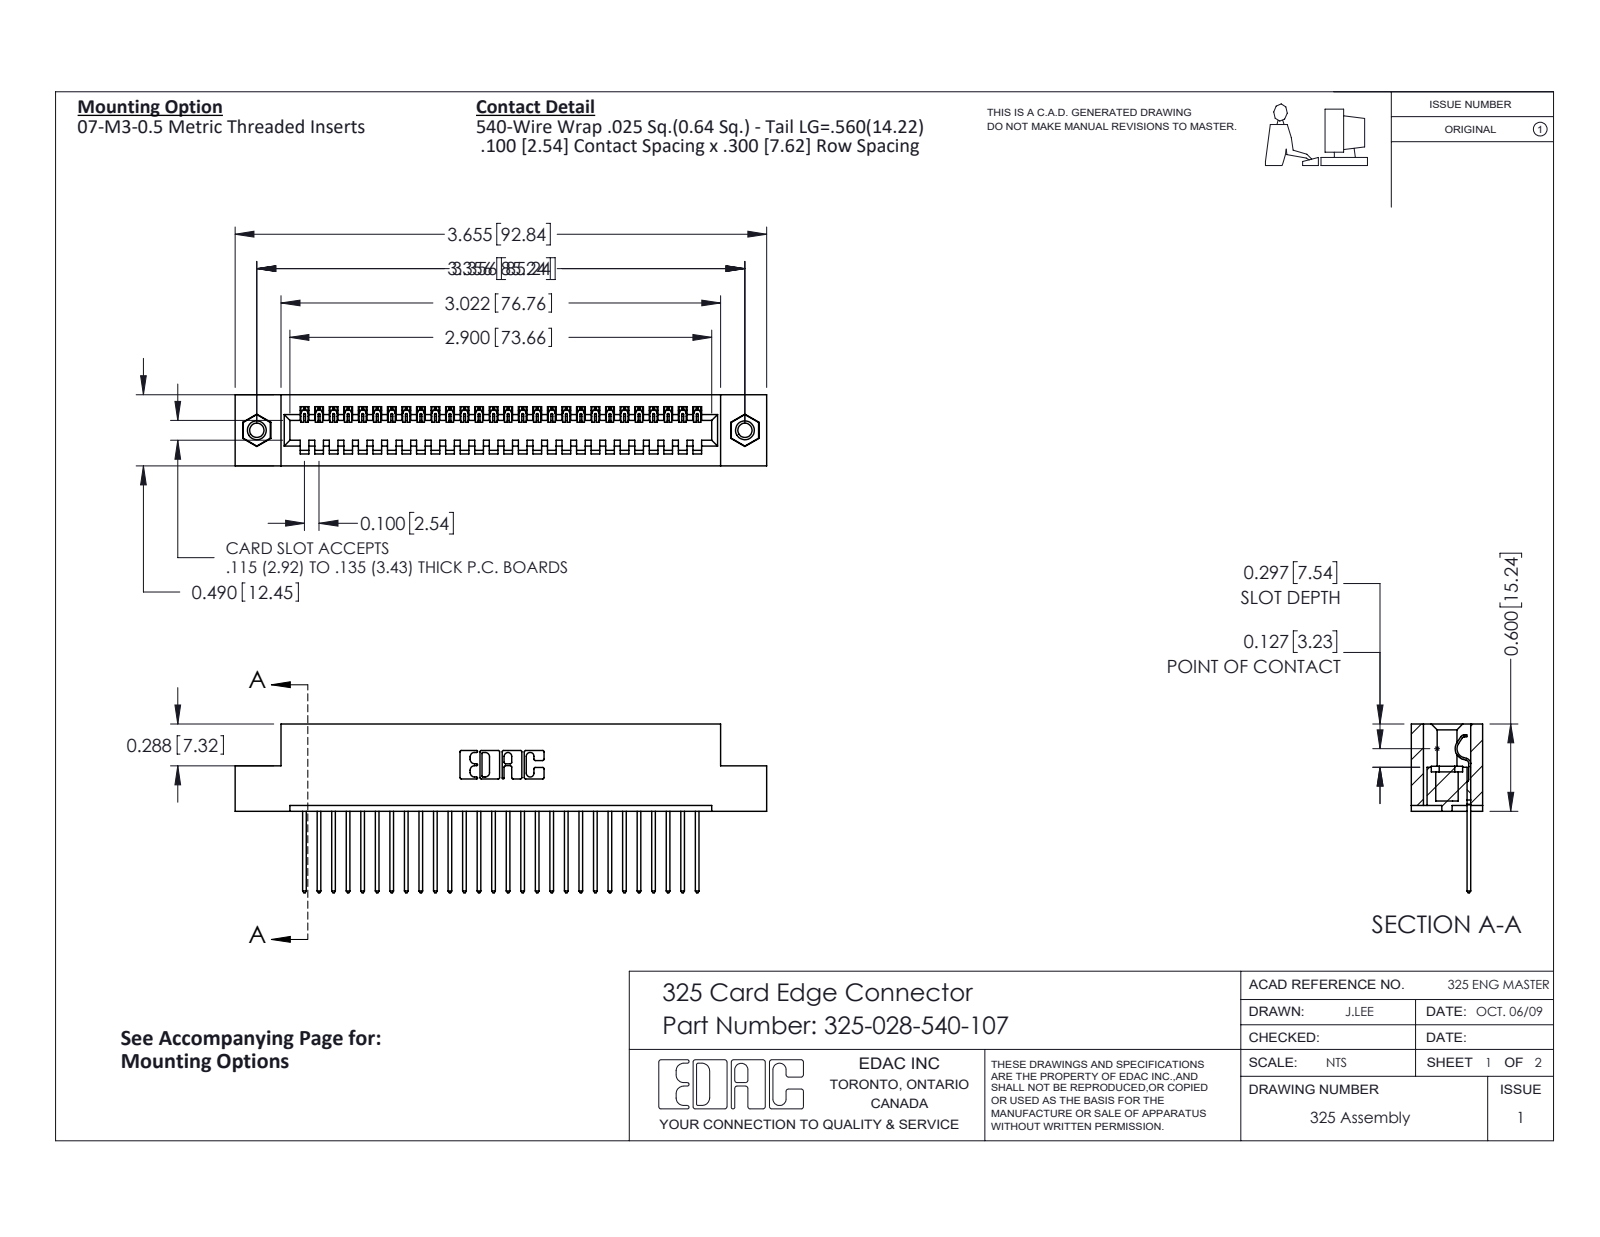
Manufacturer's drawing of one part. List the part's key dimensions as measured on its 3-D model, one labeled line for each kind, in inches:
Part name (STEP PRODUCT): 345-250-001_345-250-005-103; 325-028-540-107; 325 Part_TI; 325-292-001_325-293-140
STEP written by: SolidWorks 2016 (CONFIG_CONTROL_DESIGN)
Units: inches
Bodies: 31 solids, 1798 faces (1278 planar, 504 cylindrical, 16 other)
Overall size (bounding box): 3.655 × 1.16 × 0.49
Volume: 0.714 in³ · Surface area: 19.92 in²
Round holes (diameter × count): ⌀0.098 ×2, ⌀0.125 ×2, ⌀0.16 ×2
Round bosses / shafts (diameter × count): ⌀0.155 ×2
Partial cylindrical surfaces — rounded edges, fillets, slot ends (radius × count): R0.006 ×56, R0.01 ×56, R0.01 ×22, R0.007 ×6, R0.031 ×6, R0.026 ×3, R0.014 ×1, R0.022 ×1
Main face-to-face distances: 0.083, 0.407, 0.49, 0.3, 0.107, 0.383, 0.025, 0.325, 0.6, 0.04
Hole centre spacings: 3.356
